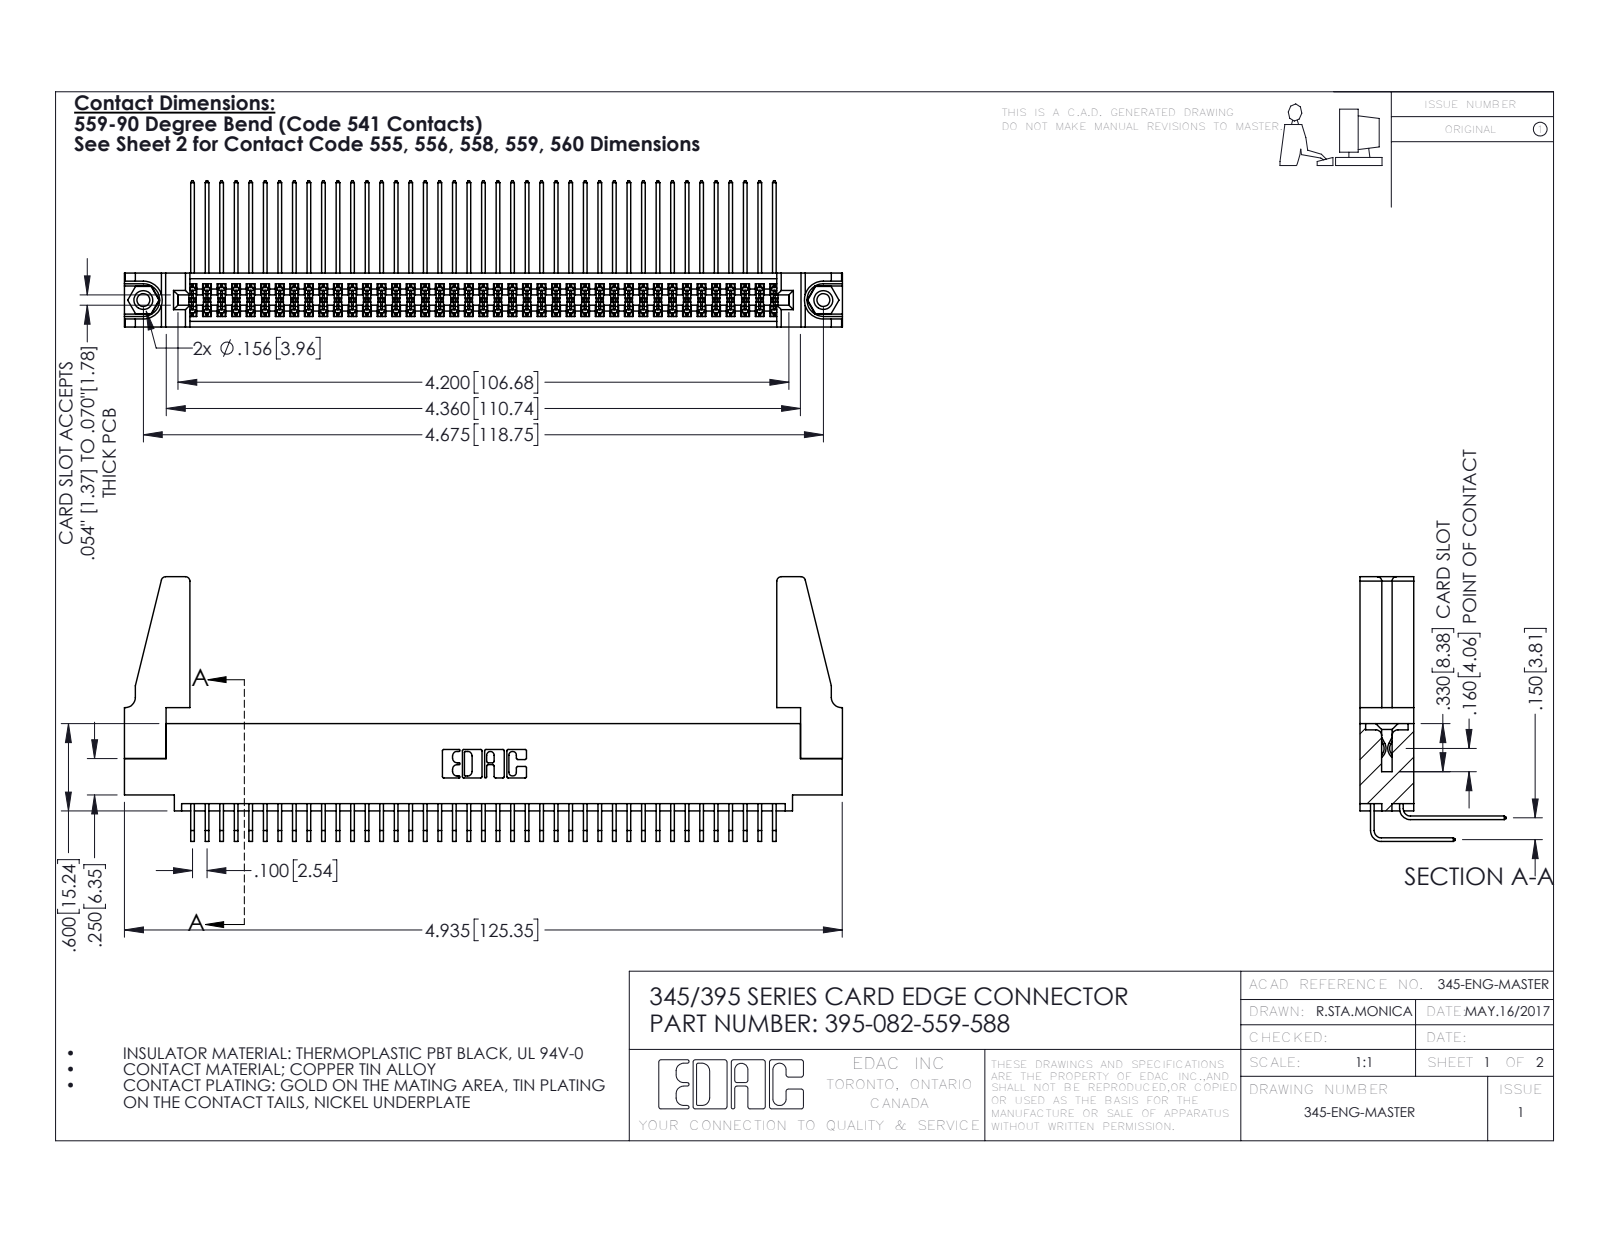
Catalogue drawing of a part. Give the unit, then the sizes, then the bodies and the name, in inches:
Units: inches
Overall size (bounding box): 4.936 × 1.819 × 1.005
Round holes (diameter × count): ⌀0.089 ×2, ⌀0.125 ×2, ⌀0.156 ×2, ⌀0.064 ×1
Round bosses / shafts (diameter × count): ⌀0.155 ×2
Partial cylindrical surfaces — rounded edges, fillets, slot ends (radius × count): R0.006 ×123, R0.01 ×22, R0.03 ×8, R0.007 ×6, R0.031 ×6, R0.026 ×3, R0.014 ×2, R0.019 ×2
Main face-to-face distances: 0.072, 0.298, 0.37, 0.2, 0.098, 0.272, 0.025, 0.225, 0.175, 0.15
Hole centre spacings: 0.27, 4.439, 4.675
Volume: 0.966 in³ · Surface area: 37.2 in²
Bodies: 87 solids, 4518 faces (3026 planar, 1476 cylindrical, 16 other)
Part name (STEP PRODUCT): 345 Part_0.110 Offset - 0.156 Dia-TH; 345-220-078_345-220-088; 345-292-001_559 Tail - 2; 345-250-001_345-250-001-102 (+2 more)
STEP written by: SolidWorks 2016 (CONFIG_CONTROL_DESIGN)
